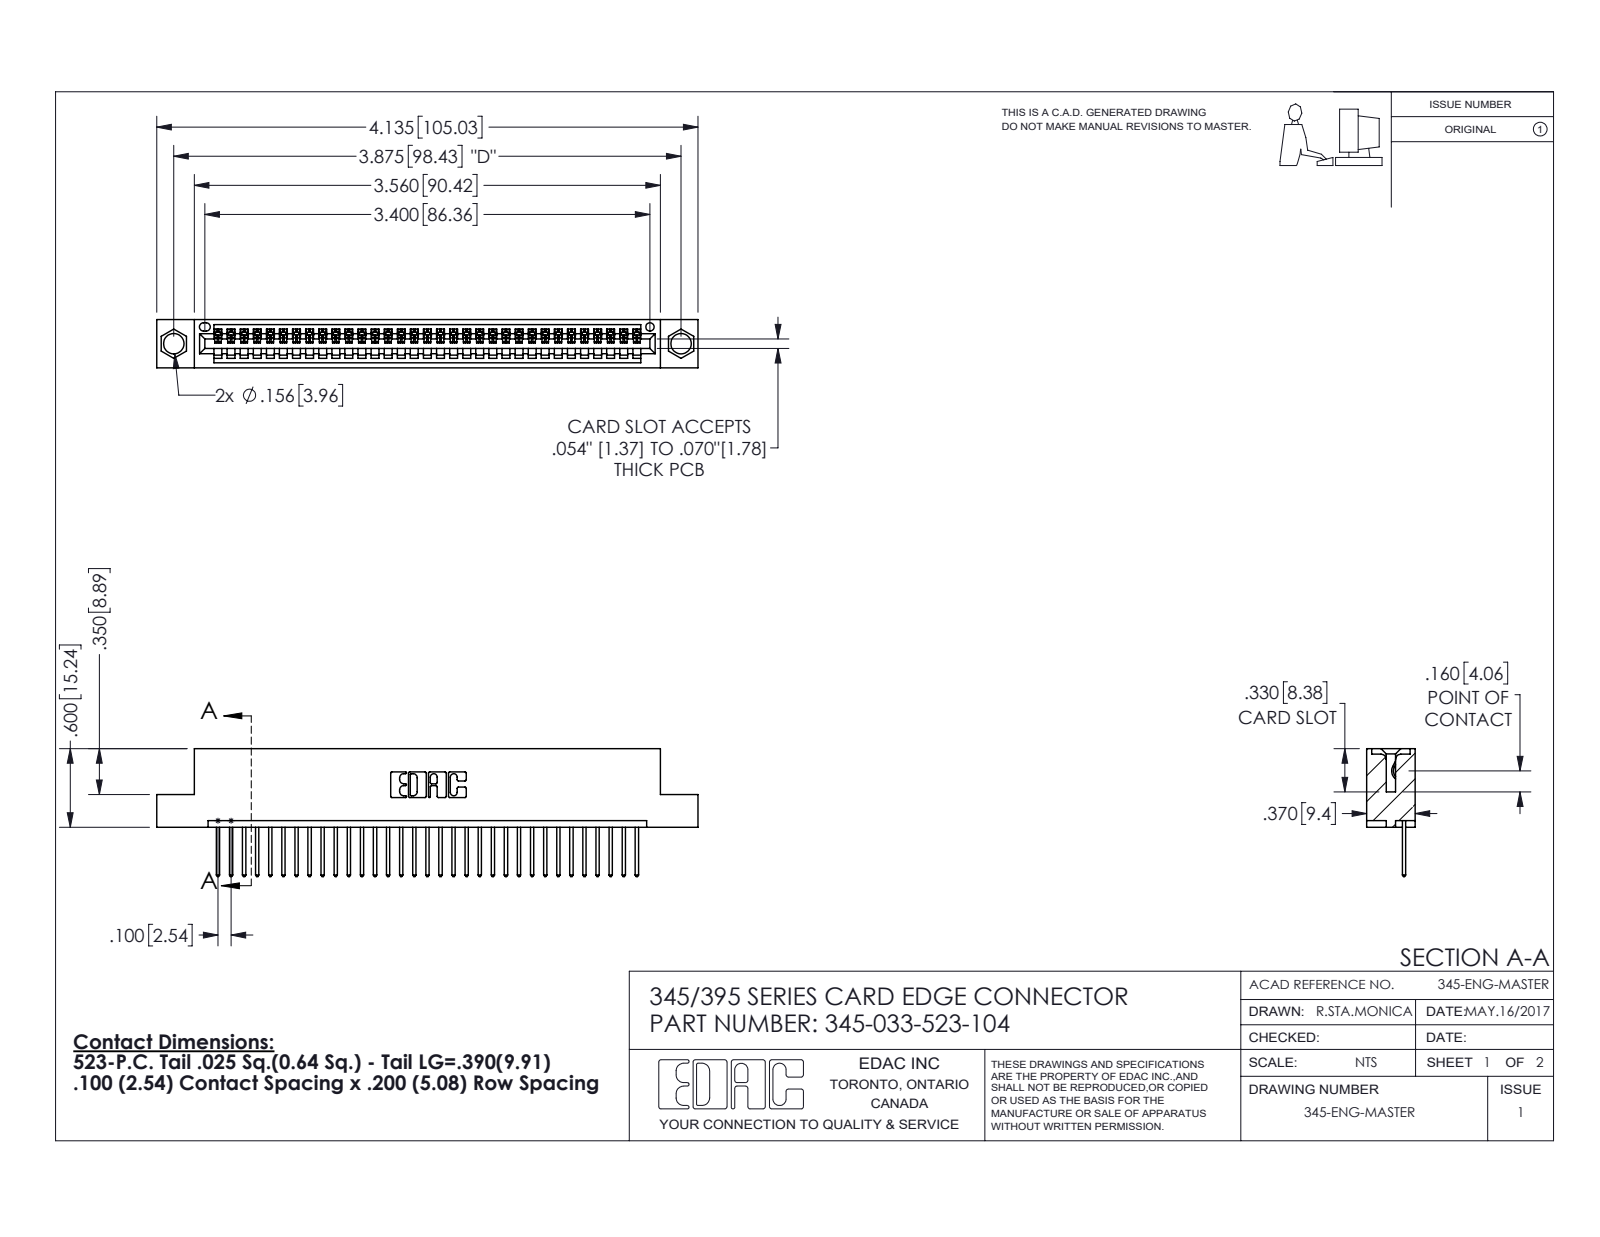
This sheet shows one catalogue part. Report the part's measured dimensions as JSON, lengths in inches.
{"part_name": "345-033-523-104; 345-292-001_345-293-123; 345 Part_Flush Mounting Lugs - 0.156 Dia-TH", "step_written_by": "SolidWorks 2016 (CONFIG_CONTROL_DESIGN)", "units": "inches", "bodies": {"solids": 34, "faces": 2040, "planar": 1400, "cylindrical": 640, "other": 0}, "overall_size": [4.135, 0.977, 0.37], "volume_in3": 0.598, "surface_area_in2": 19.76, "round_holes": [[0.156, 2], [0.064, 1]], "partial_cylinders_radius": [[0.006, 66], [0.01, 66], [0.01, 22], [0.007, 6], [0.031, 6], [0.026, 3], [0.031, 2], [0.04, 2]], "face_to_face_distances": [0.298, 0.072, 0.2, 0.37, 0.098, 0.272, 0.025, 0.225, 0.149, 0.072], "hole_center_spacings": [0.27, 3.64, 3.875]}
